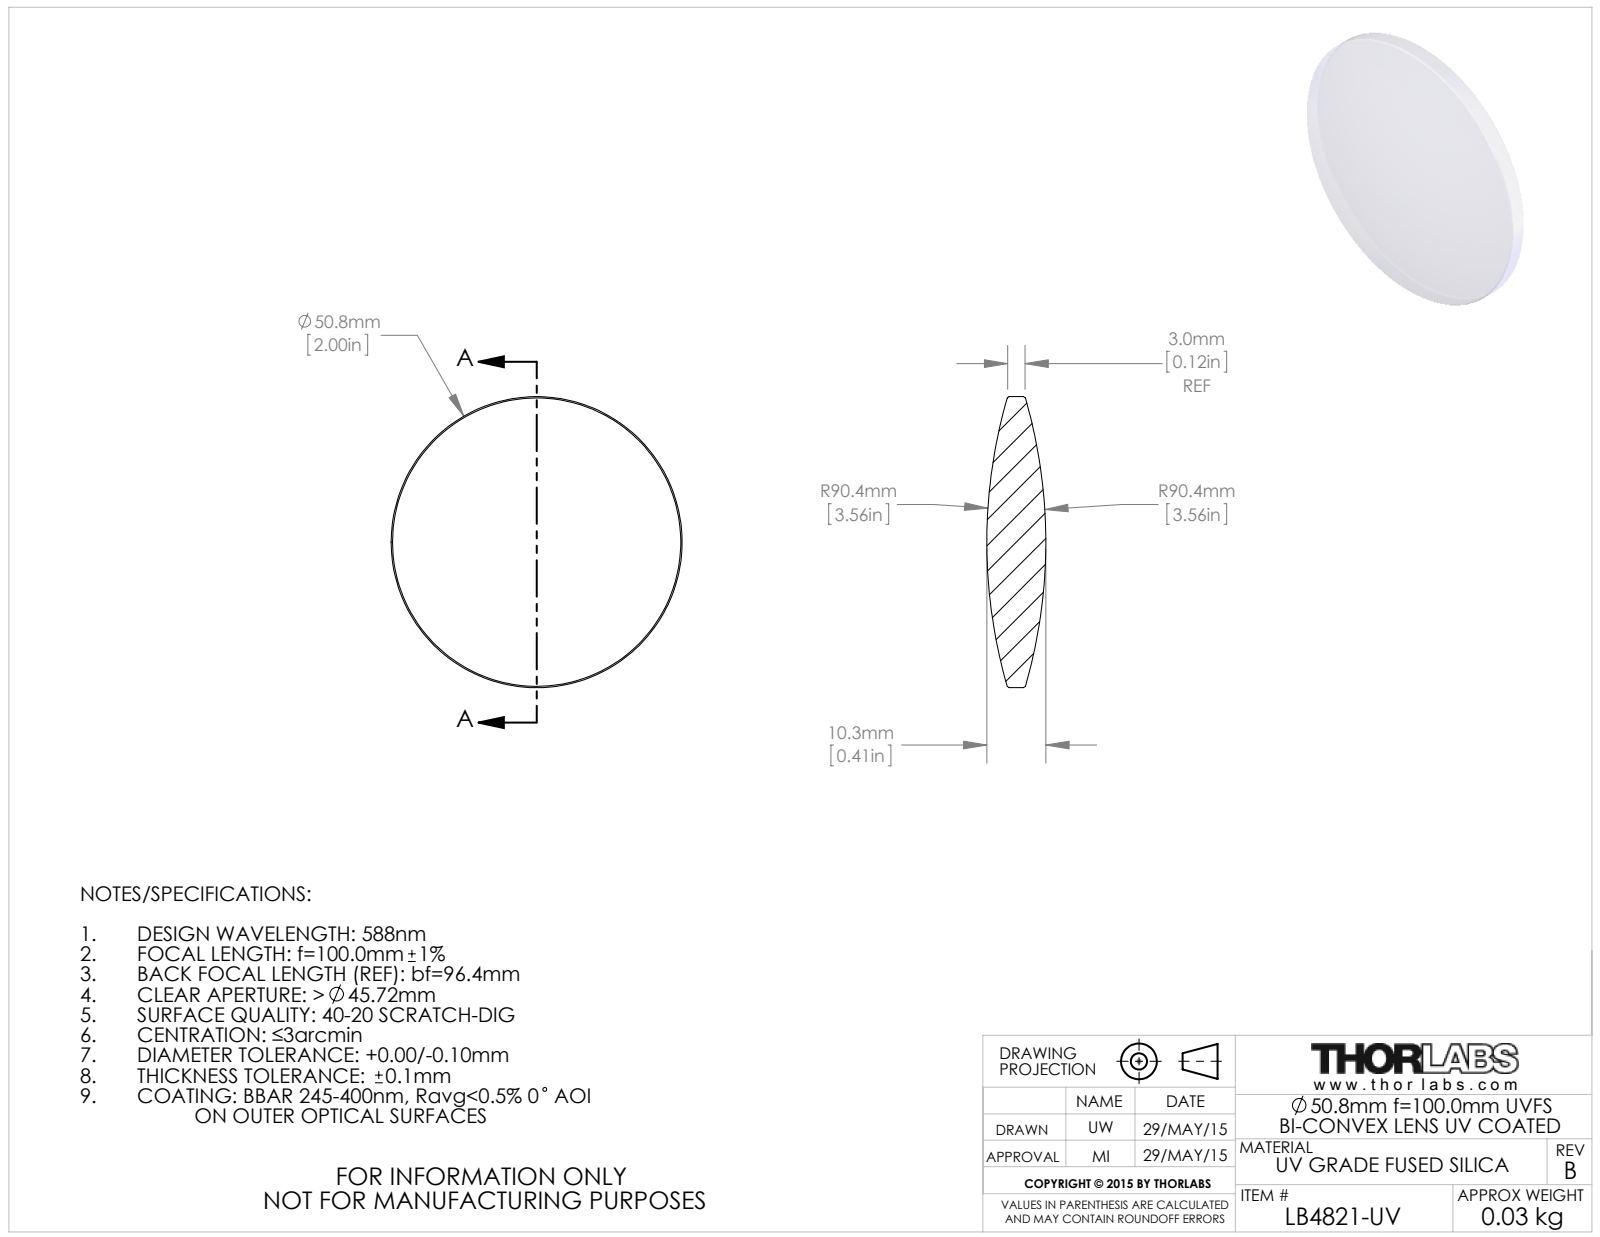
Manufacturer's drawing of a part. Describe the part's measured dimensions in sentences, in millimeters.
The part is named "4333-E0W". Its 3-D file was written by "SolidWorks 2014 (CONFIG_CONTROL_DESIGN)". It is 1 solid with 10 faces: 0 planar, 2 cylindrical and 8 other. Overall it measures 50.8 by 50.8 by 10.3 millimeters. Its volume is 13 536 cubic millimeters and its surface area 4 586 square millimeters. Round bosses or shafts: 1 of diameter 50.8.
